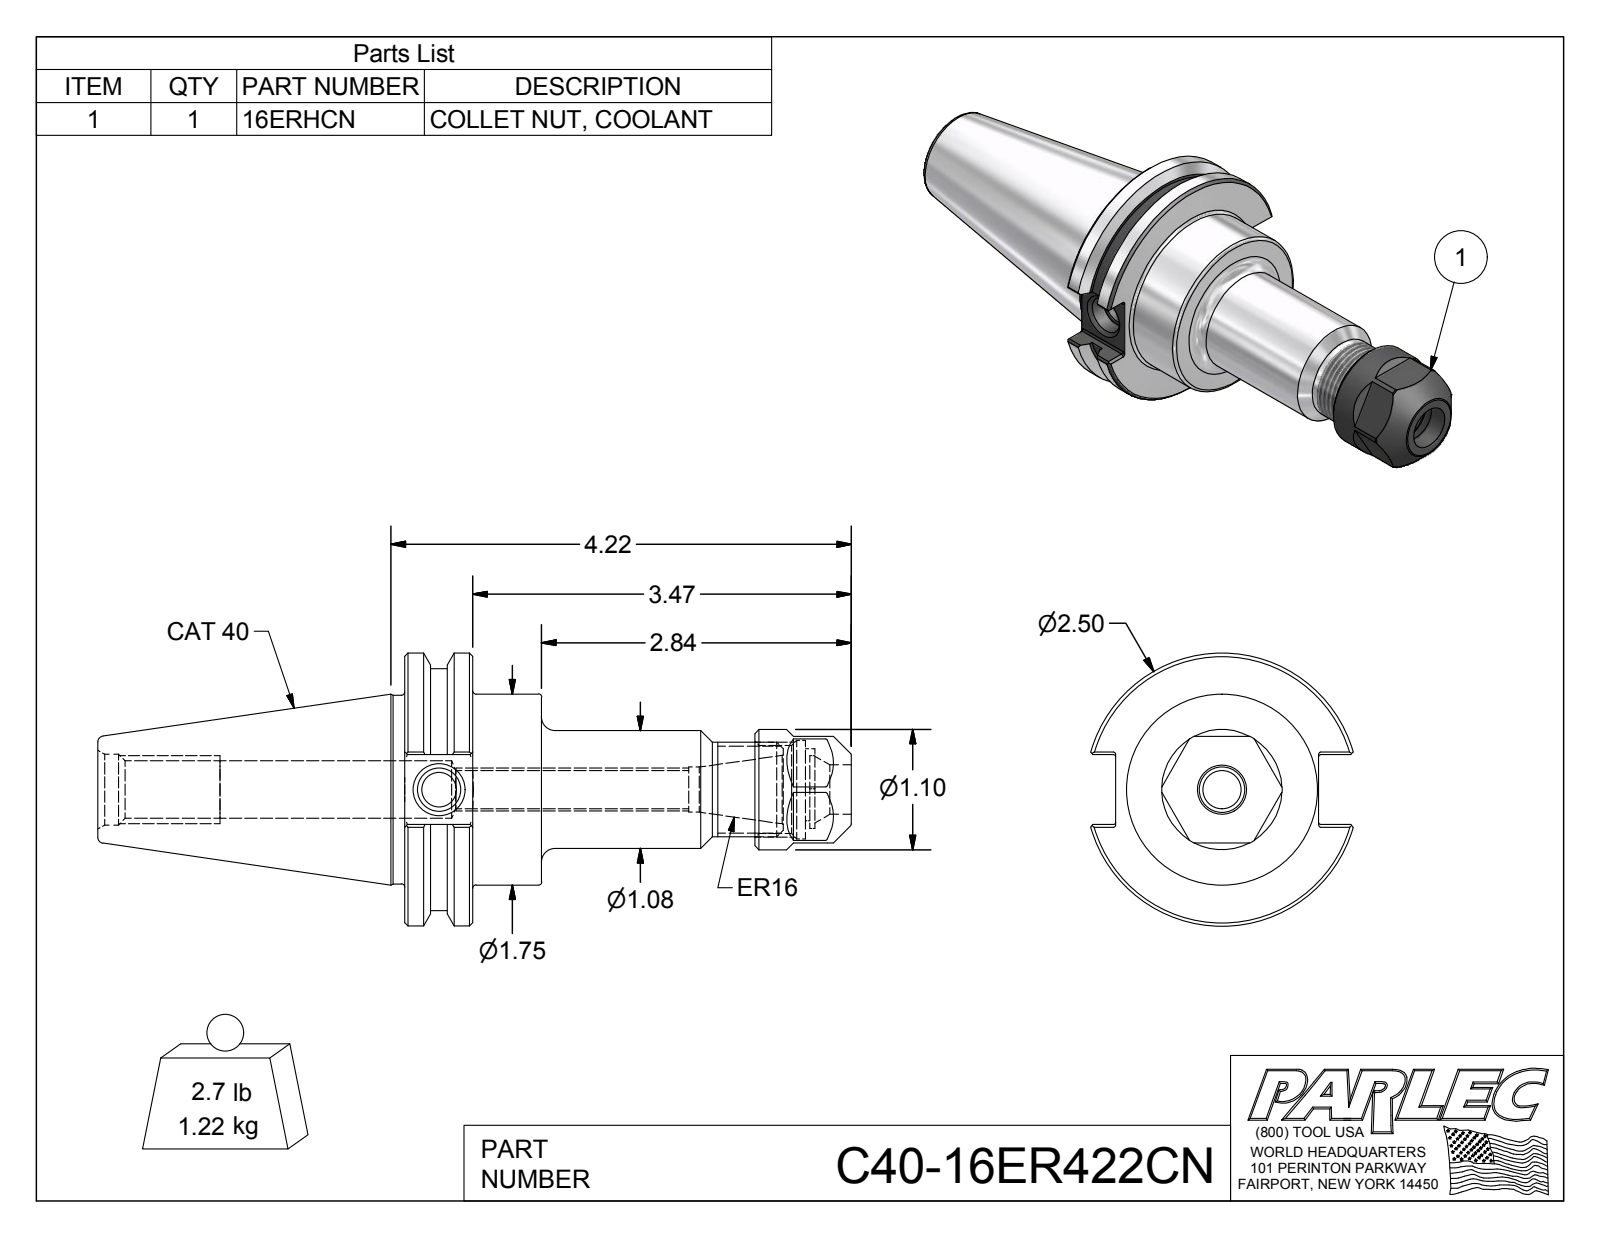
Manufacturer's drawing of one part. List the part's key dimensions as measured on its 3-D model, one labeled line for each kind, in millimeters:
Part name (STEP PRODUCT): C40-16ER422CN; C40-16ER4-1; 16ERHCN
STEP written by: Autodesk Inventor 2012 (AUTOMOTIVE_DESIGN)
Units: millimetres
Bodies: 2 solids, 122 faces (50 planar, 35 cylindrical, 37 other)
Overall size (bounding box): 175.5 × 63.5 × 61
Volume: 155 200 mm³ · Surface area: 32 750 mm²
Round holes (diameter × count): ⌀8 ×1, ⌀8.9 ×1, ⌀10.1 ×1, ⌀10.5 ×1, ⌀11.5 ×1, ⌀13.4 ×1, ⌀13.4 ×1, ⌀16.5 ×1, ⌀16.8 ×1, ⌀20.5 ×1, ⌀23 ×1
Round bosses / shafts (diameter × count): ⌀63.5 ×1, ⌀56.4 ×1, ⌀44.5 ×1, ⌀43.9 ×1, ⌀28 ×1, ⌀27.4 ×1, ⌀22 ×1
Partial cylindrical surfaces — rounded edges, fillets, slot ends (radius × count): R0.5 ×12, R9 ×1
Main face-to-face distances: 15.9, 31.9, 16, 24.9, 4.3, 20.5, 93.3, 77.4, 61.4, 16.3
Hole centre spacings: 1.3
